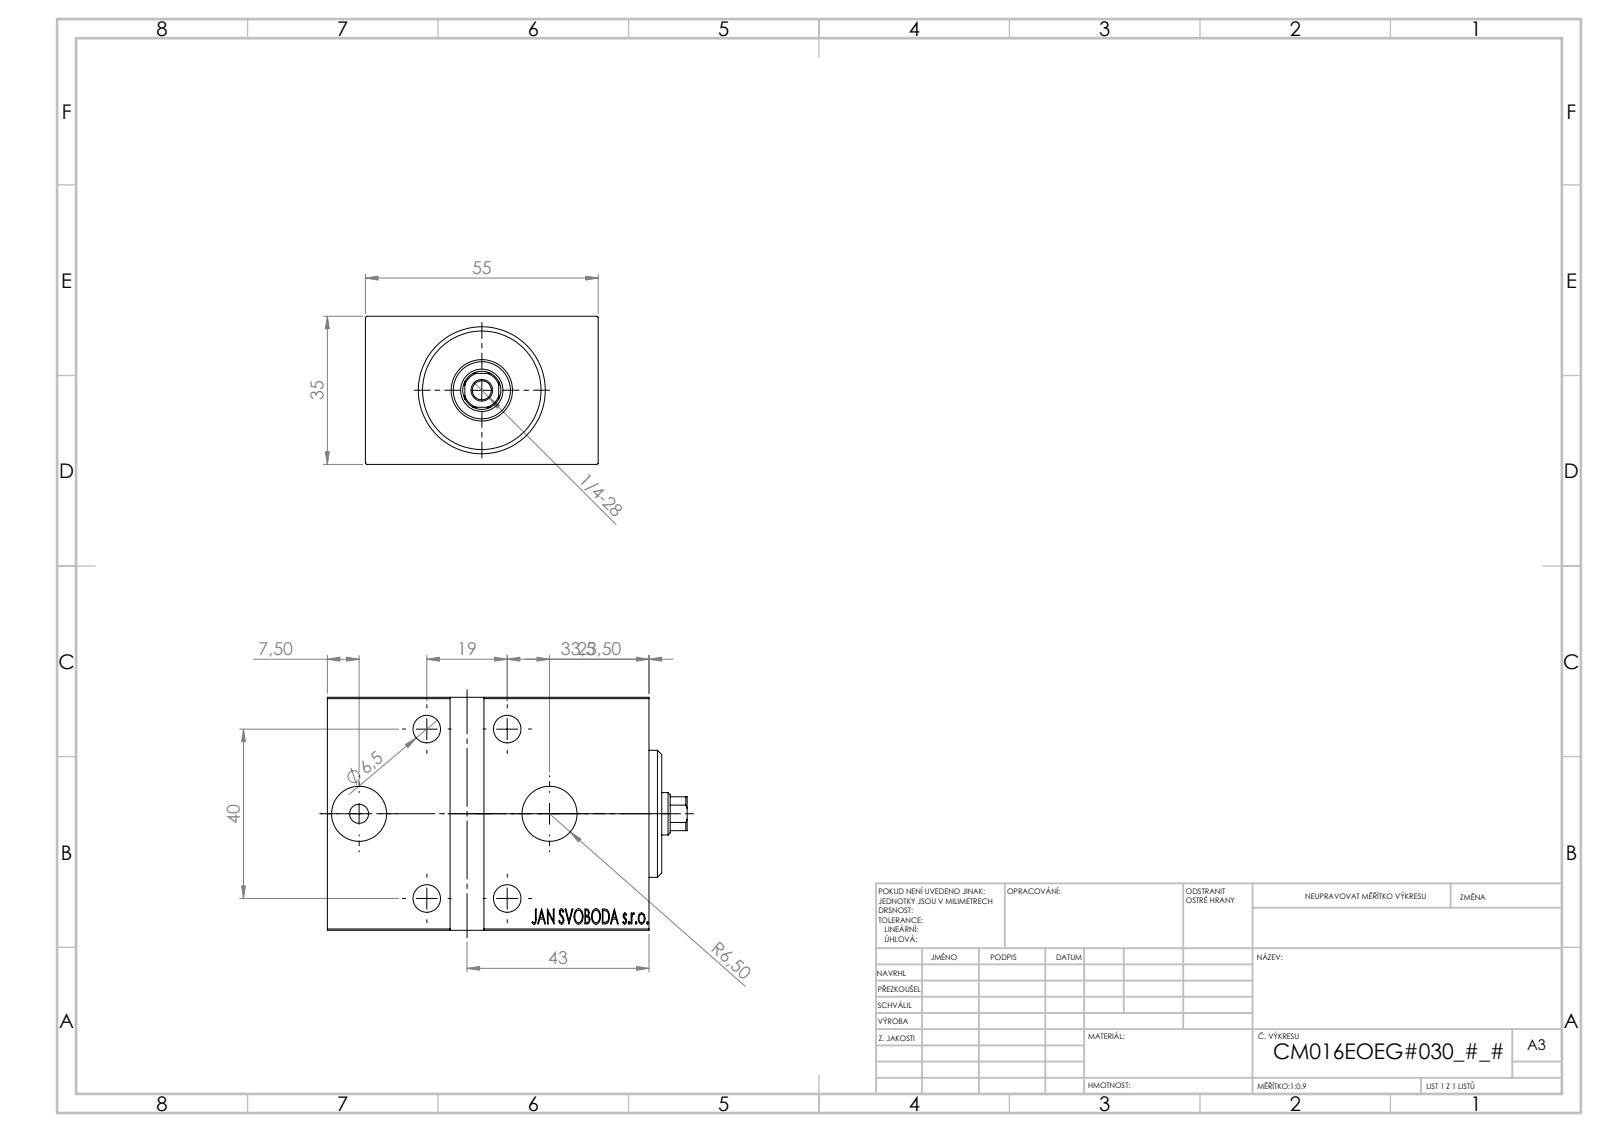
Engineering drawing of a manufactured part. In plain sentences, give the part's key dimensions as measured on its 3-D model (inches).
The part is named "V450CM_VC_B; V450CM_E_Body; V450CM_E_VCP". Its 3-D file was written by "SolidWorks 2019 (CONFIG_CONTROL_DESIGN)". It is 3 solids with 852 faces: 410 planar, 48 cylindrical and 394 other. Overall it measures 3.346 by 2.165 by 1.378 inches. Its volume is 8.443 cubic inches and its surface area 48.8 square inches. Round holes: 4 of diameter 0.256, 4 of diameter 0.413, 2 of diameter 0.512, 1 of diameter 0.177, 1 of diameter 0.394, 1 of diameter 0.531, 1 of diameter 0.571, 1 of diameter 0.63, 1 of diameter 0.984. Round bosses or shafts: 1 of diameter 1.181, 1 of diameter 0.709, 1 of diameter 0.177. Partial cylindrical surfaces (rounded edges, fillets, slot ends): 1 of radius 0.177. The main face-to-face distances are 1.378, 2.165, 2.992, 0.197, 2.795, 0.315, 0.039, 1.339, 0.118, 3.11. The hole center spacings are 0.748, 0.88, 1.008, 1.387, 1.575, 1.587, 1.743, 1.772.
